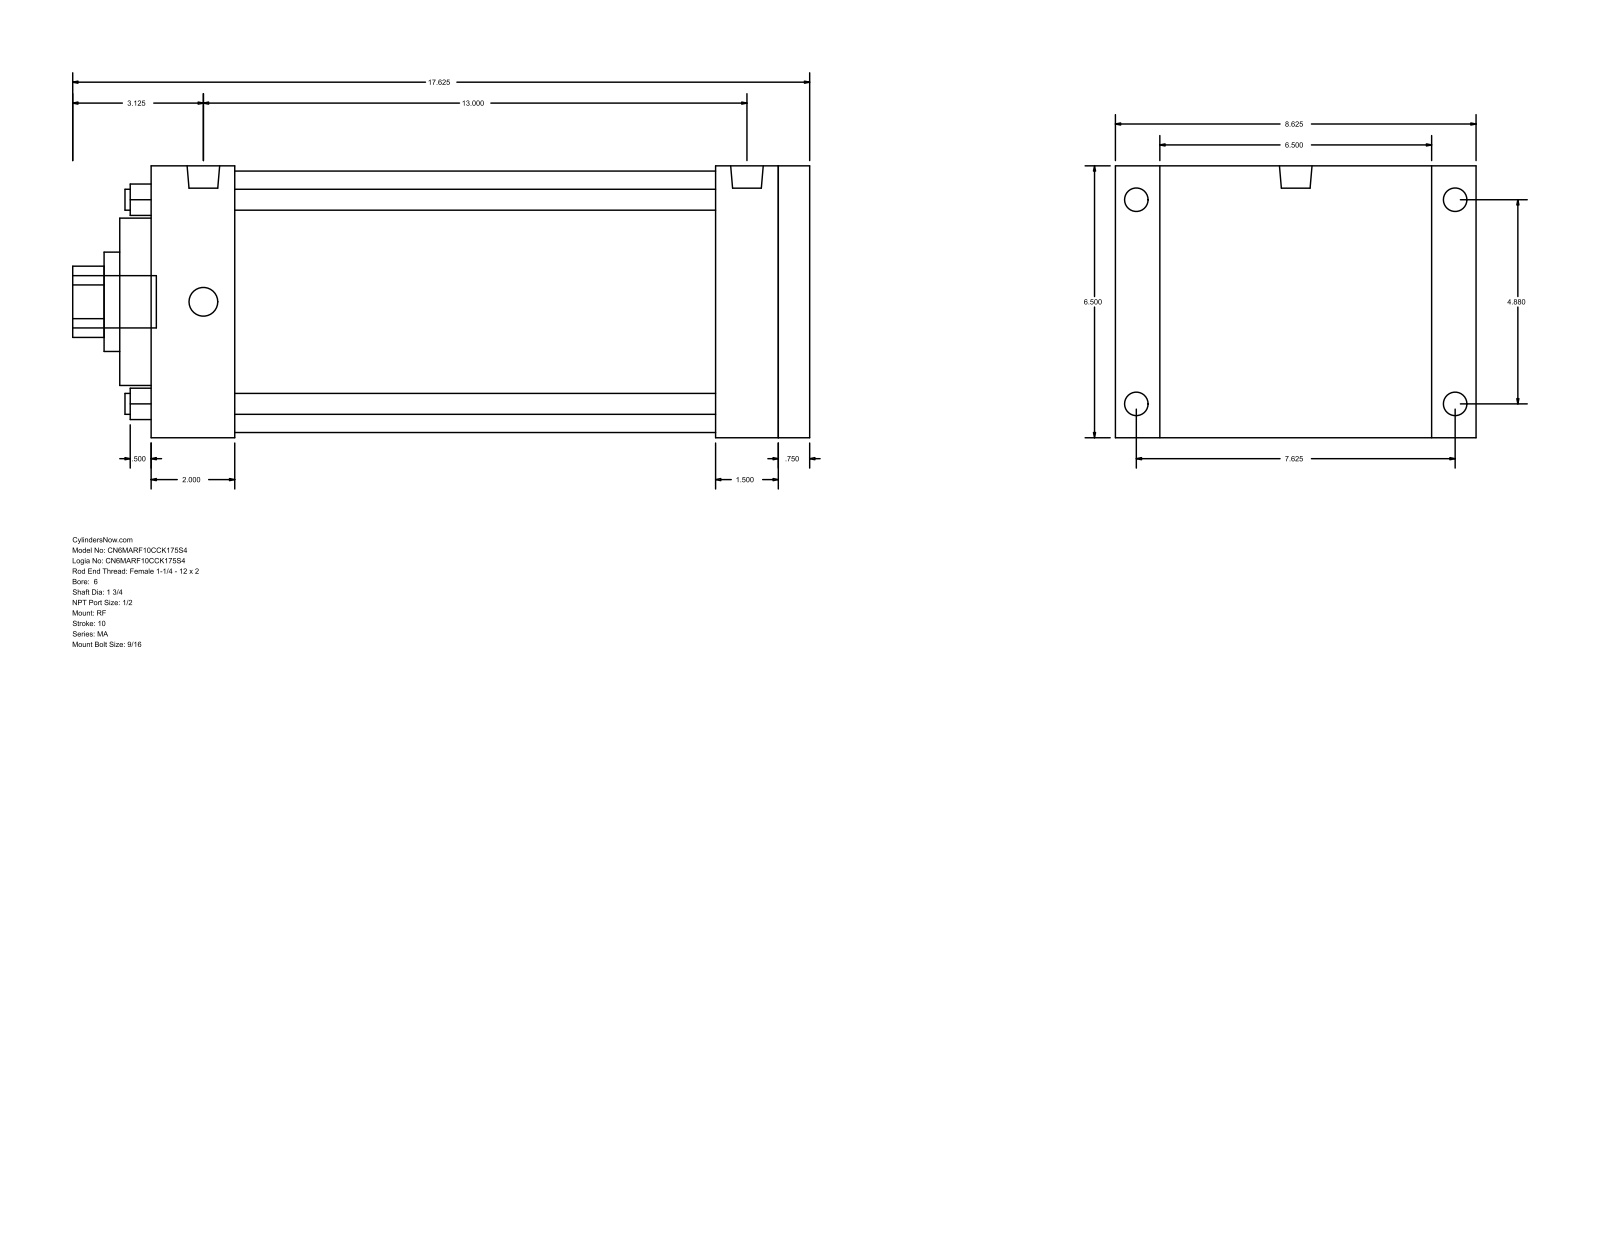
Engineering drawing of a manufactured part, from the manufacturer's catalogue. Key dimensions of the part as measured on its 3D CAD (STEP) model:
Part name (STEP PRODUCT): MA_RF__0600_1.75
STEP written by: GSSL Pune (CONFIG_CONTROL_DESIGN)
Units: millimetres
Bodies: 0 solids, 94 faces (65 planar, 29 cylindrical, 0 other)
Overall size (bounding box): 447.68 × 219.07 × 165.1
Round holes (diameter × count): ⌀12.7 ×4, ⌀44.45 ×1, ⌀60.33 ×1, ⌀101.6 ×1, ⌀158.75 ×1
Round bosses / shafts (diameter × count): ⌀17.46 ×4, ⌀14.29 ×4, ⌀19.77 ×2, ⌀31.75 ×1
Partial cylindrical surfaces — rounded edges, fillets, slot ends (radius × count): R21.63 ×1
Main face-to-face distances: 165.1, 400.06, 381, 19.06, 19.05, 38.1, 50.8, 330.2, 349.26, 342.9
Hole centre spacings: 87.65, 123.96, 175.31
